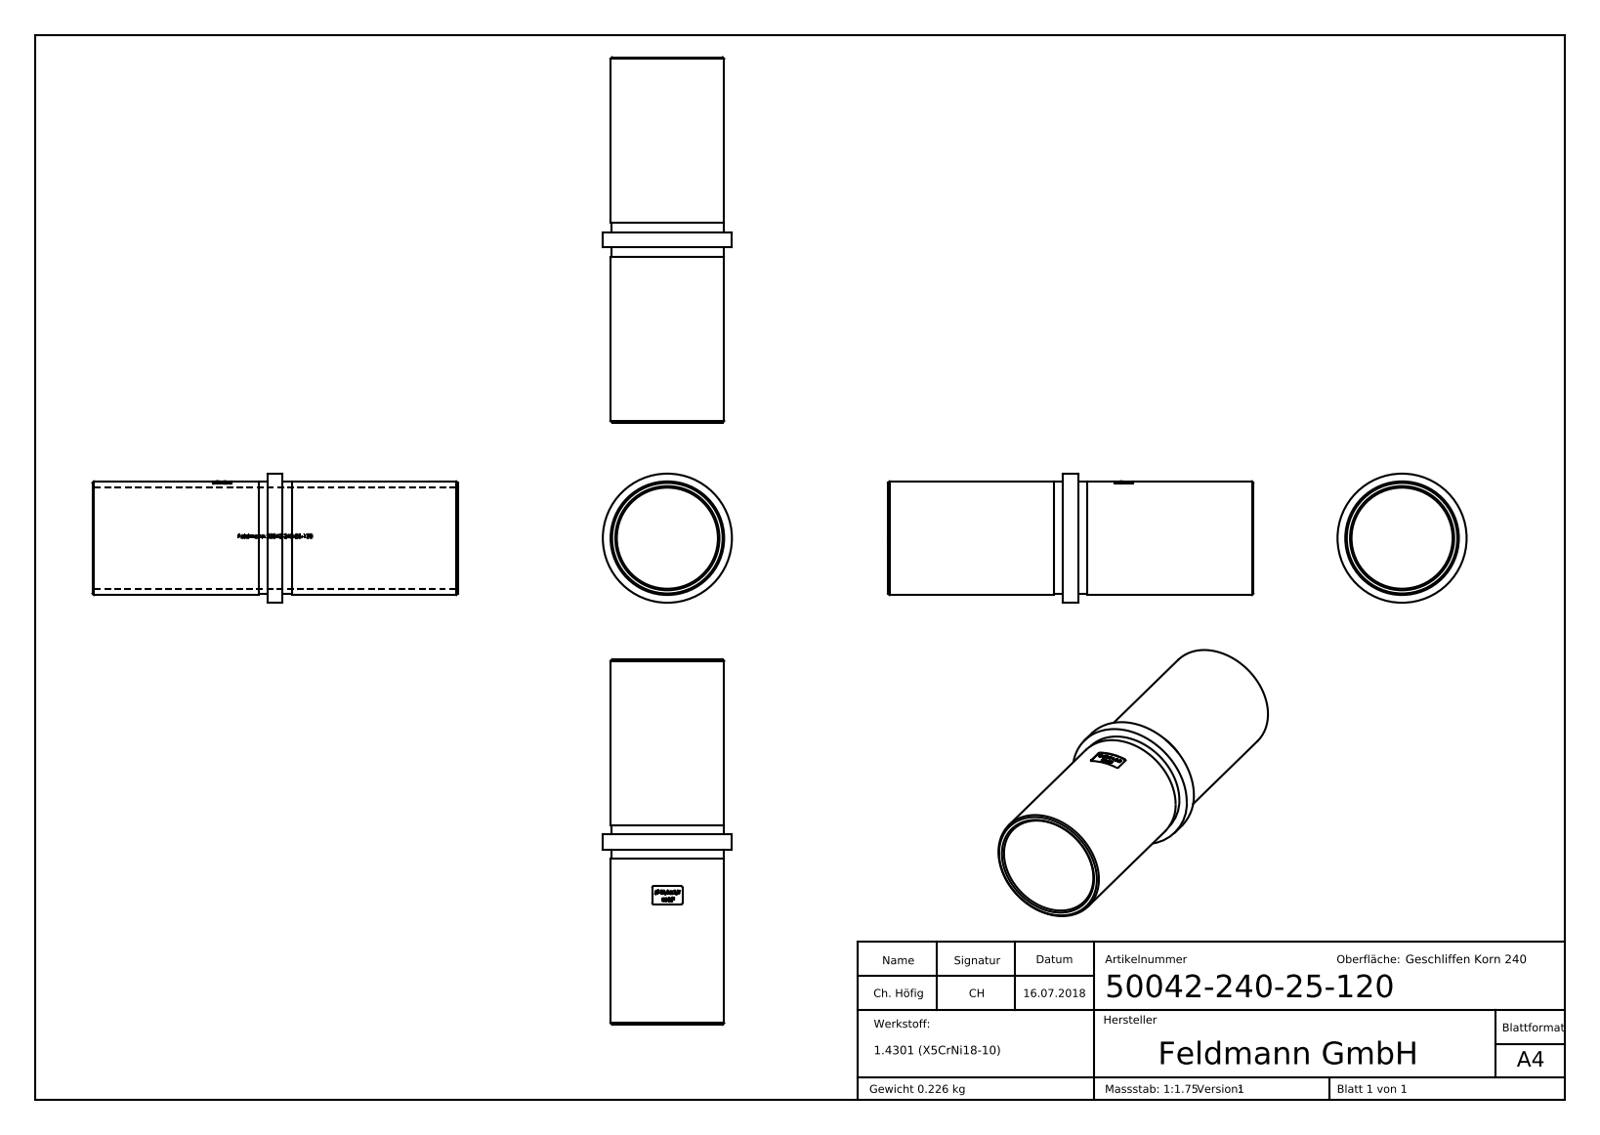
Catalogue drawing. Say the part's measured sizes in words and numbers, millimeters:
The part is named "50042-240-25-120". Its 3-D file was written by "SolidWorks 2015 (CONFIG_CONTROL_DESIGN)". It is 1 solid with 512 faces: 248 planar, 75 cylindrical and 189 other. Overall it measures 120 by 42.4 by 42.4 millimeters. Its volume is 28 636 cubic millimeters and its surface area 27 728 square millimeters. Round holes: 1 of diameter 33.2. Round bosses or shafts: 1 of diameter 42.4, 1 of diameter 37.3, 1 of diameter 36.9. Partial cylindrical surfaces (rounded edges, fillets, slot ends): 4 of radius 0.5, 1 of radius 16.7, 1 of radius 18.55. The main face-to-face distances are 5, 57.5, 62.5, 120, 54.5, 65.5, 3, 8, 11, 80.5.
